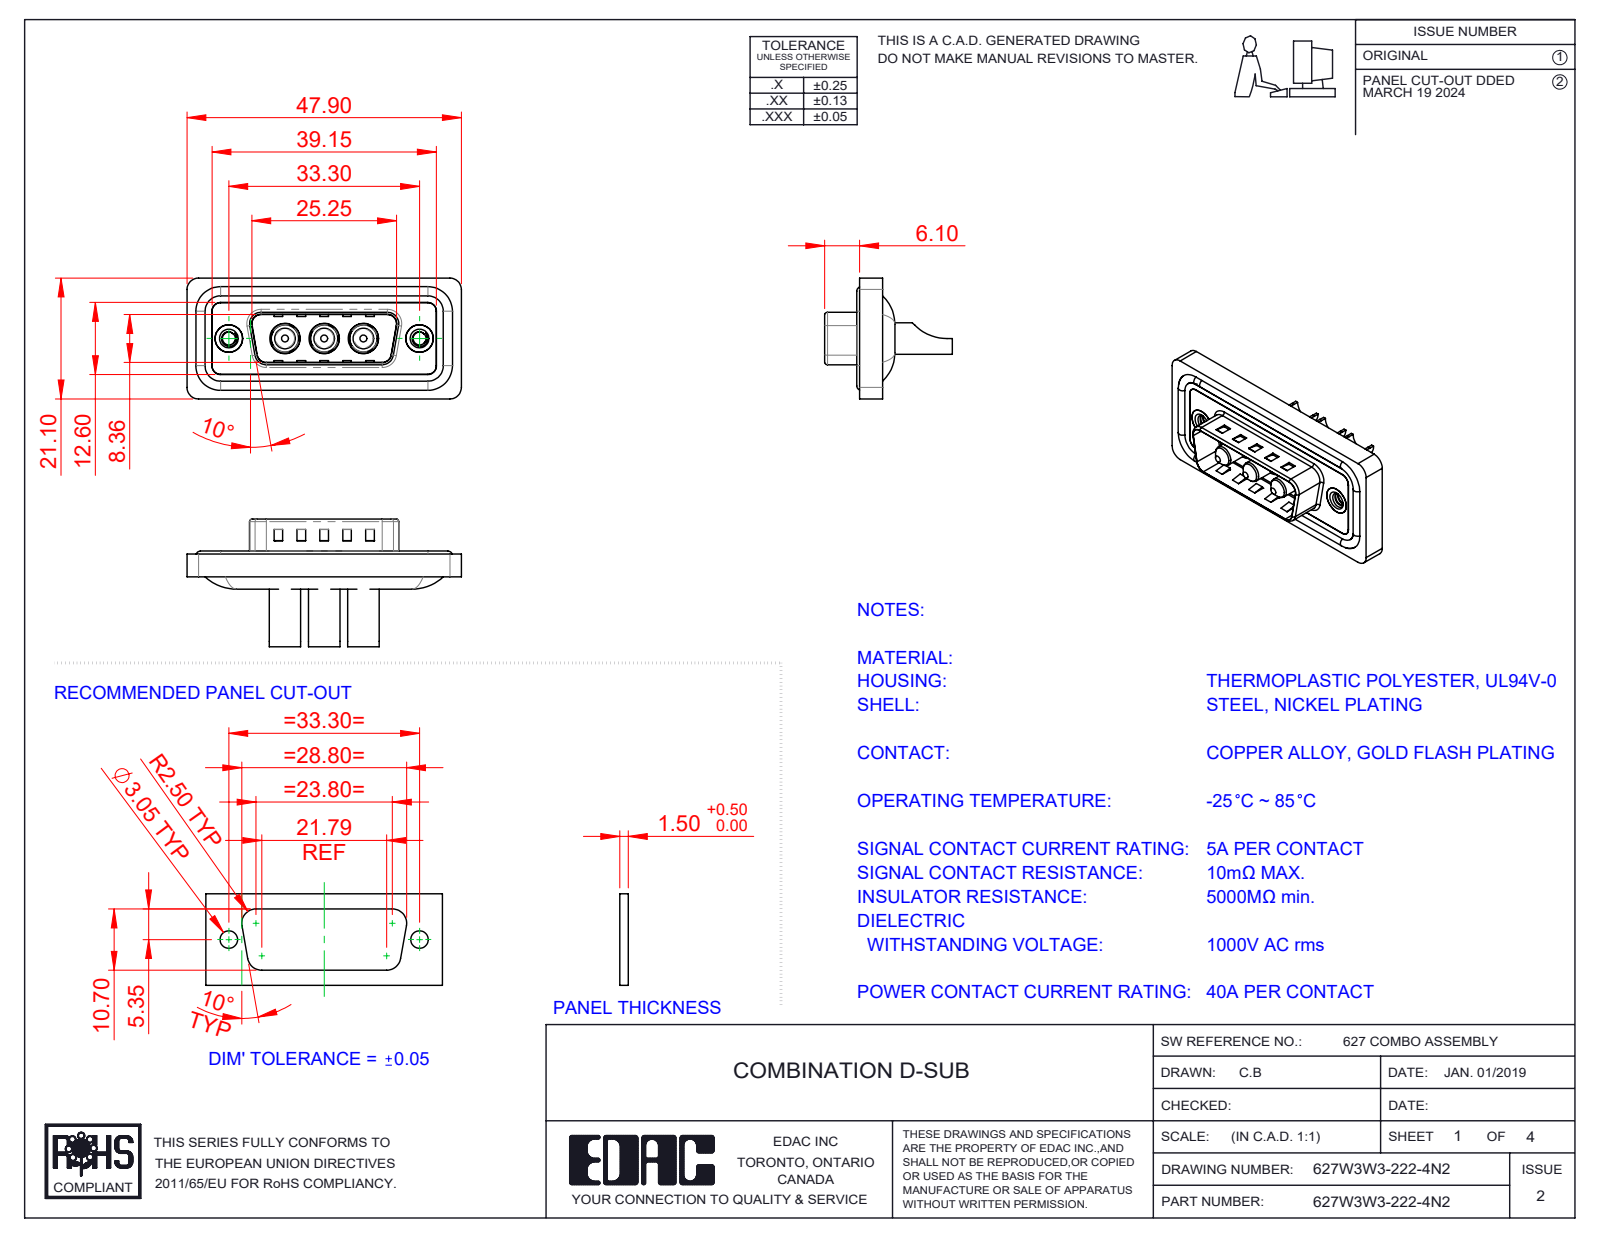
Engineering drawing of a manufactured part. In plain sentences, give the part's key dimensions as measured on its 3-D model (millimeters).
The part is named "Power Pin_40A SC; 627Combo Shell Rear_15 Contacts; 627Combo Shell Front_15 Contacts; 627Combo Waterproof Housing_15 Contacts (+3 more)". Its 3-D file was written by "SolidWorks 2023 (CONFIG_CONTROL_DESIGN)". It is 13 solids with 576 faces: 213 planar, 244 cylindrical and 119 other. Overall it measures 47.9 by 22.3 by 21.1 millimeters. Its volume is 5 705 cubic millimeters and its surface area 9 173 square millimeters. Round holes: 3 of diameter 4.6, 3 of diameter 4.85, 3 of diameter 5.3, 2 of diameter 2.26, 2 of diameter 4, 2 of diameter 4.8, 2 of diameter 5. Round bosses or shafts: 4 of diameter 1.6, 3 of diameter 5.5, 3 of diameter 5.2, 3 of diameter 4.75, 3 of diameter 3.75, 3 of diameter 3.6, 2 of diameter 4.9. Partial cylindrical surfaces (rounded edges, fillets, slot ends): 26 of radius 1.5, 20 of radius 2, 8 of radius 0.5, 8 of radius 1.6, 4 of radius 0.25, 4 of radius 0.6, 4 of radius 0.65, 4 of radius 0.9. The main face-to-face distances are 0.4, 1.1, 0.5, 1.6, 3.1, 2.9, 1.5, 0.82, 9.58, 2.5. The hole center spacings are 6.85, 9.8, 16.65, 23.5, 13.7, 33.3.
